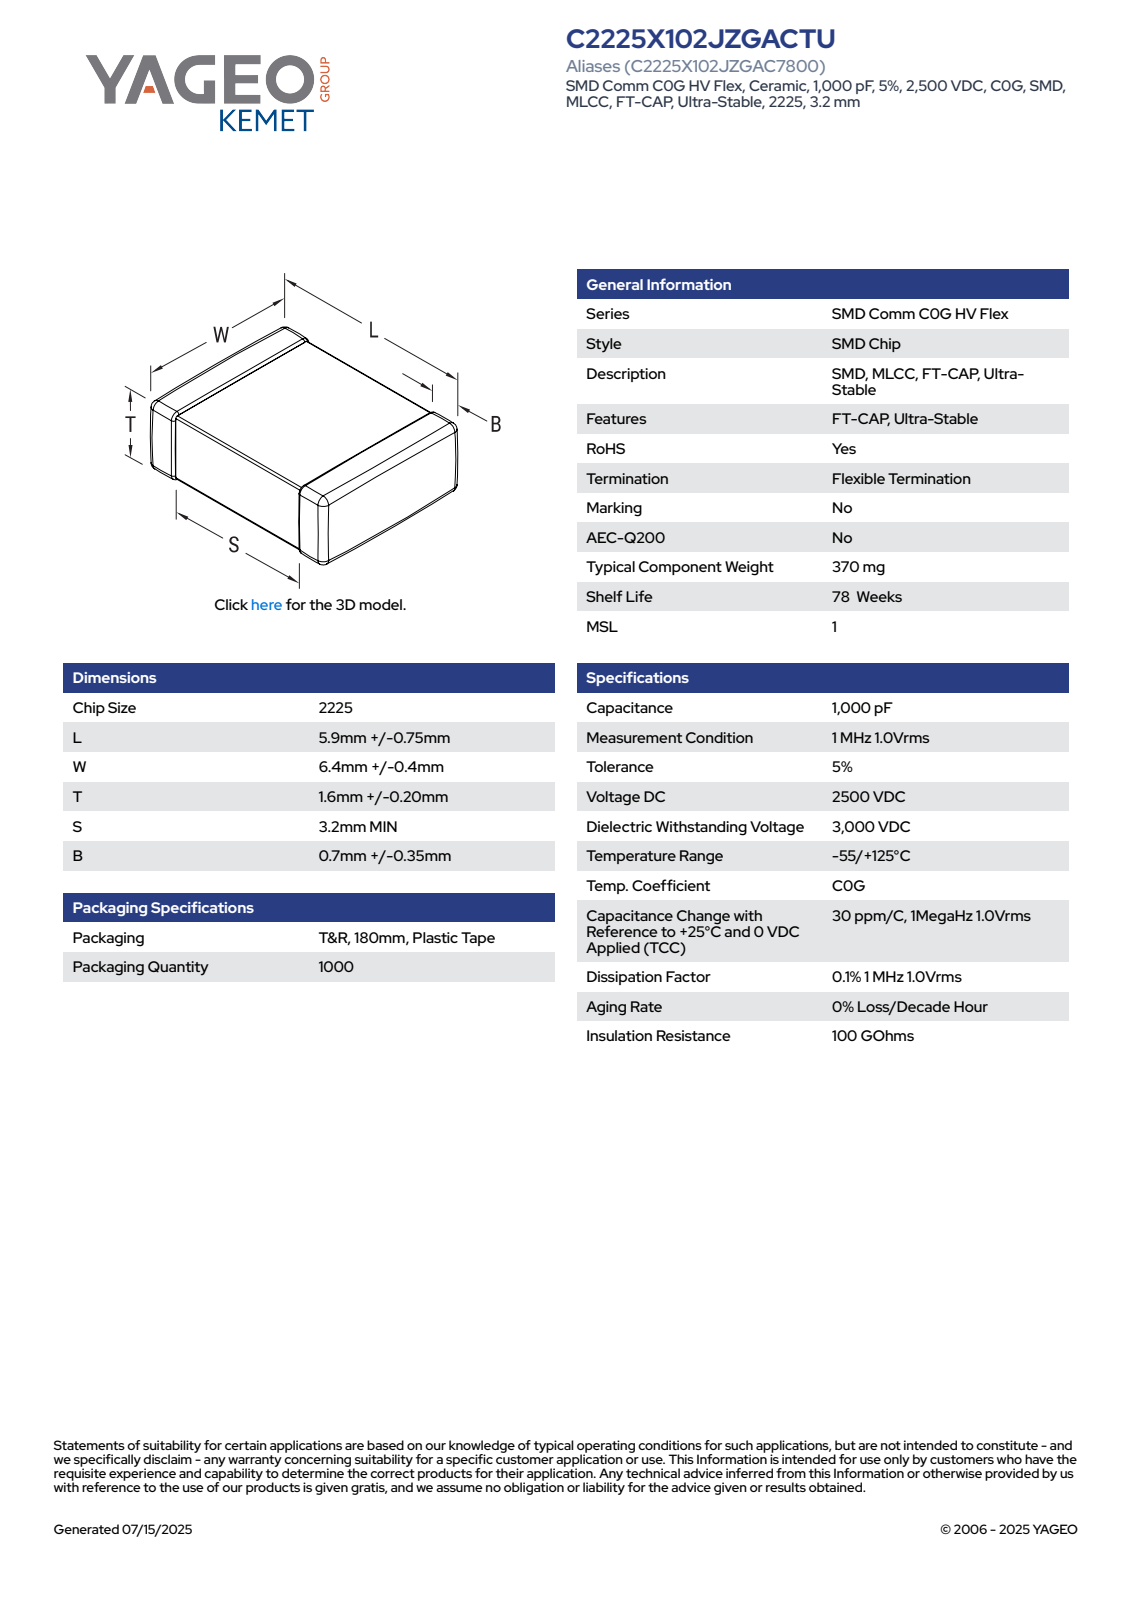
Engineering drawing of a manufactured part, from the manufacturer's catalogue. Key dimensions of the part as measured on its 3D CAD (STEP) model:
Part name (STEP PRODUCT): CCS_CCSTDNOS_2225_L6.65W6.8T1.8B1.05
STEP written by: SolidWorks 2014 (AUTOMOTIVE_DESIGN)
Units: millimetres
Bodies: 4 solids, 121 faces (71 planar, 34 cylindrical, 16 other)
Overall size (bounding box): 6.8 × 6.65 × 1.8
Volume: 70 mm³ · Surface area: 134 mm²
Partial cylindrical surfaces — rounded edges, fillets, slot ends (radius × count): R0.14 ×24
Main face-to-face distances: 1.52, 1.66, 1.8, 6.65, 6.52, 6.66, 6.8, 3.29, 3.37, 0.47
